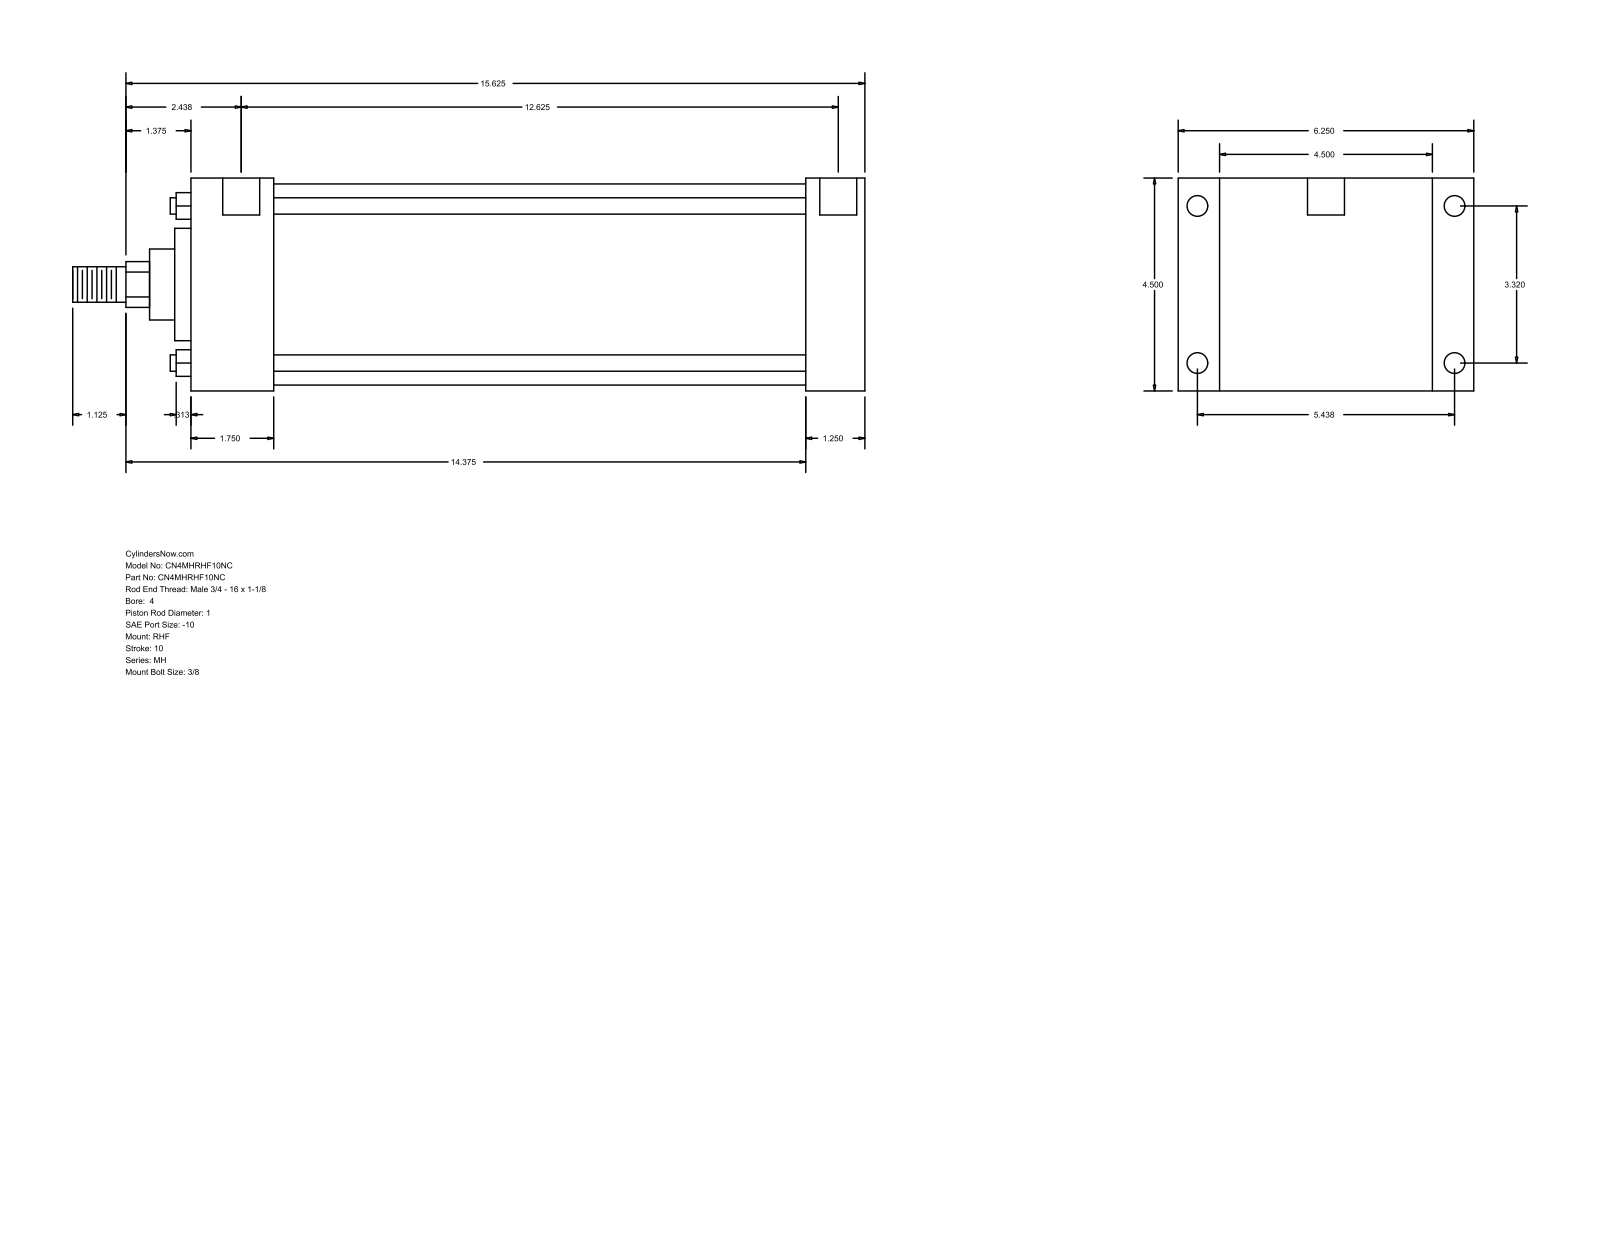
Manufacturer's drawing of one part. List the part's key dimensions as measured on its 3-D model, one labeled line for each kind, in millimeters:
Part name (STEP PRODUCT): MH_RHF__0400_1
STEP written by: GSSL Pune (CONFIG_CONTROL_DESIGN)
Units: millimetres
Bodies: 0 solids, 90 faces (61 planar, 29 cylindrical, 0 other)
Overall size (bounding box): 425.45 × 158.75 × 114.3
Round holes (diameter × count): ⌀8.73 ×4, ⌀11.13 ×4, ⌀19.84 ×2
Round bosses / shafts (diameter × count): ⌀8.76 ×4, ⌀107.95 ×1, ⌀60.33 ×1, ⌀38.1 ×1, ⌀25.4 ×1, ⌀19.05 ×1
Partial cylindrical surfaces — rounded edges, fillets, slot ends (radius × count): R12.29 ×1
Main face-to-face distances: 114.3, 361.96, 330.2, 31.76, 22.23, 136.53, 44.46, 285.74, 317.5, 158.76
Hole centre spacings: 84.32, 138.12, 161.82, 323.85, 1.58, 1.59, 320.68, 322.26
